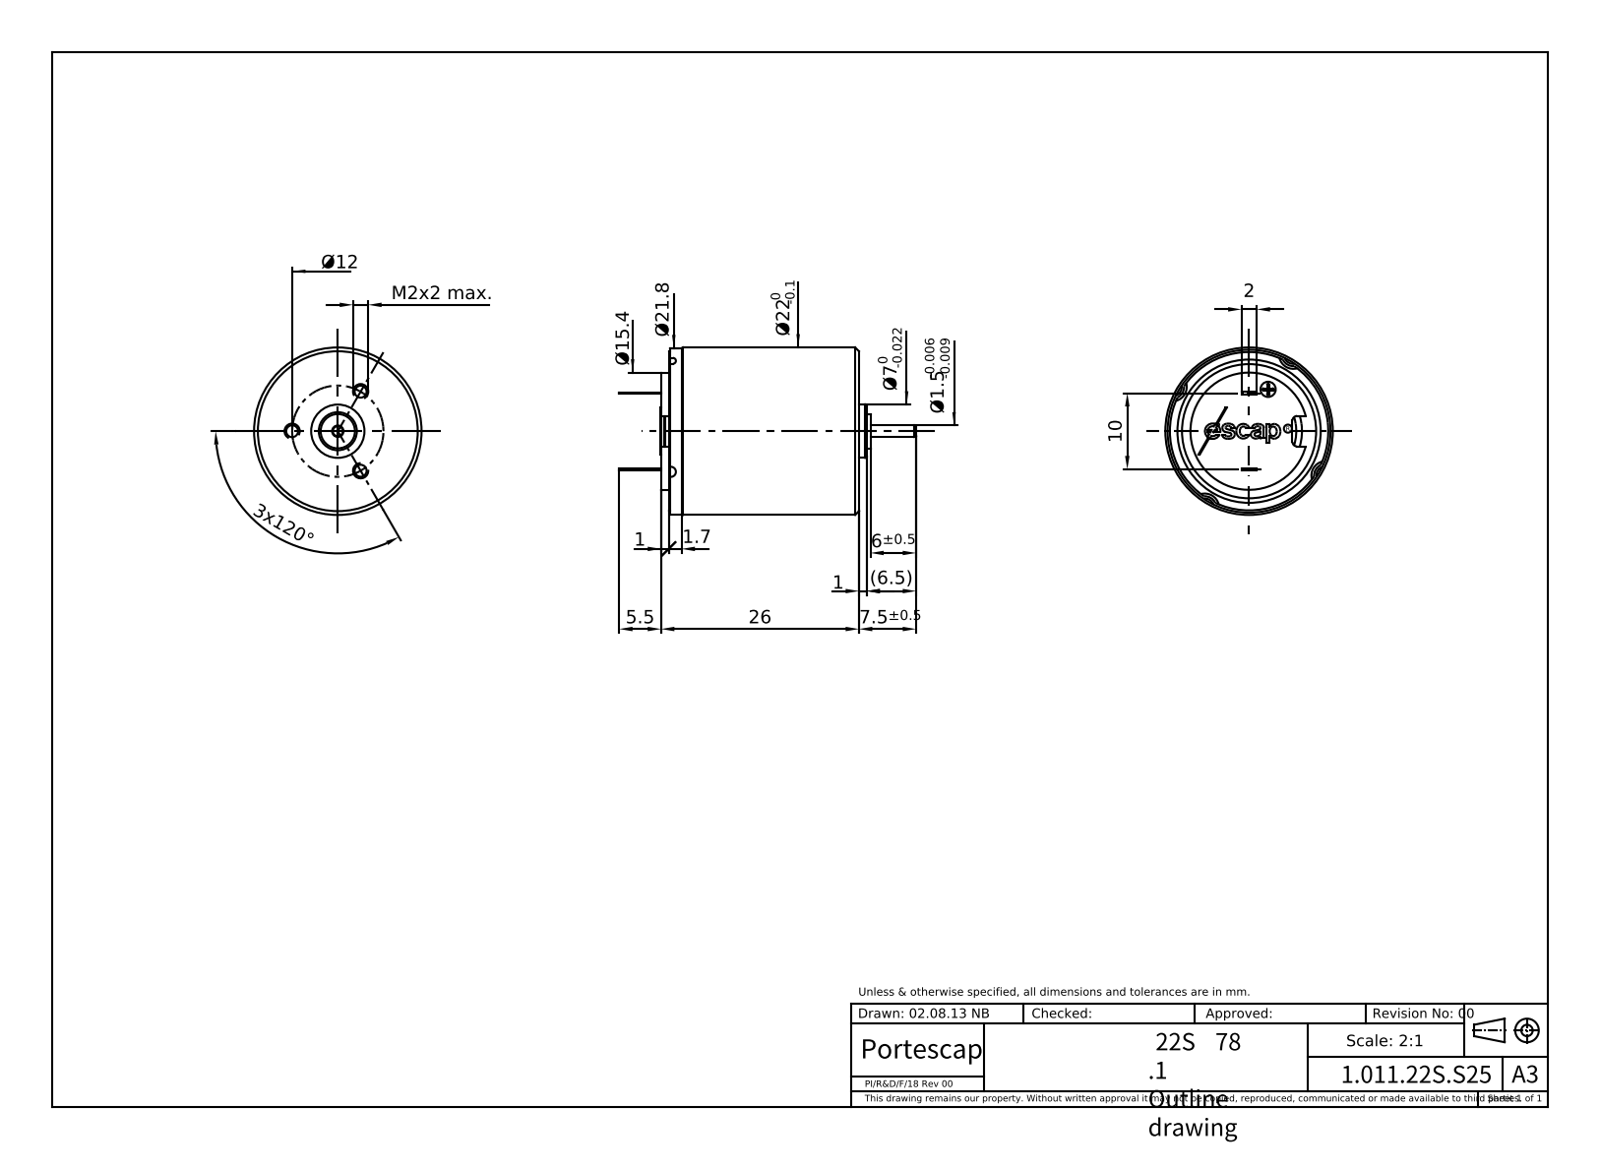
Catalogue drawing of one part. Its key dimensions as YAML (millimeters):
part_name: "22S-78_ASM"
step_written_by: "PRO/ENGINEER BY PARAMETRIC TECHNOLOGY CORPORATION, 2014310 (CONFIG_CONTROL_DESIGN)"
units: millimeters
bodies: {solids: 1, faces: 459, planar: 220, cylindrical: 132, other: 107}
overall_size: [39, 22, 22]
volume: 9481
surface_area: 3896
round_holes:
  - {diameter: 1.6, count: 10}
  - {diameter: 2, count: 6}
  - {diameter: 2.5, count: 2}
  - {diameter: 1.5, count: 1}
  - {diameter: 1.53, count: 1}
  - {diameter: 2.2, count: 1}
  - {diameter: 5, count: 1}
  - {diameter: 15.4, count: 1}
  - {diameter: 21, count: 1}
  - {diameter: 21.2, count: 1}
round_bosses_or_shafts:
  - {diameter: 22, count: 1}
  - {diameter: 21.8, count: 1}
  - {diameter: 20.9, count: 1}
  - {diameter: 10.8, count: 1}
  - {diameter: 7, count: 1}
  - {diameter: 4.52, count: 1}
  - {diameter: 4.5, count: 1}
  - {diameter: 3.6, count: 1}
partial_cylinders:
  - {radius: 0.5, count: 17}
  - {radius: 0.2, count: 4}
  - {radius: 0.4, count: 4}
  - {radius: 0.6, count: 4}
  - {radius: 1, count: 4}
  - {radius: 1.4, count: 4}
  - {radius: 1.75, count: 2}
  - {radius: 0.72, count: 1}
face_to_face_distances: [26, 0.7, 0.5, 1.6, 24.4, 1.1, 1, 2.3, 23.7, 0.6]
hole_center_spacings: [6, 2.64, 3.38, 4.96, 7.49, 8.08, 10.39, 10.48]
